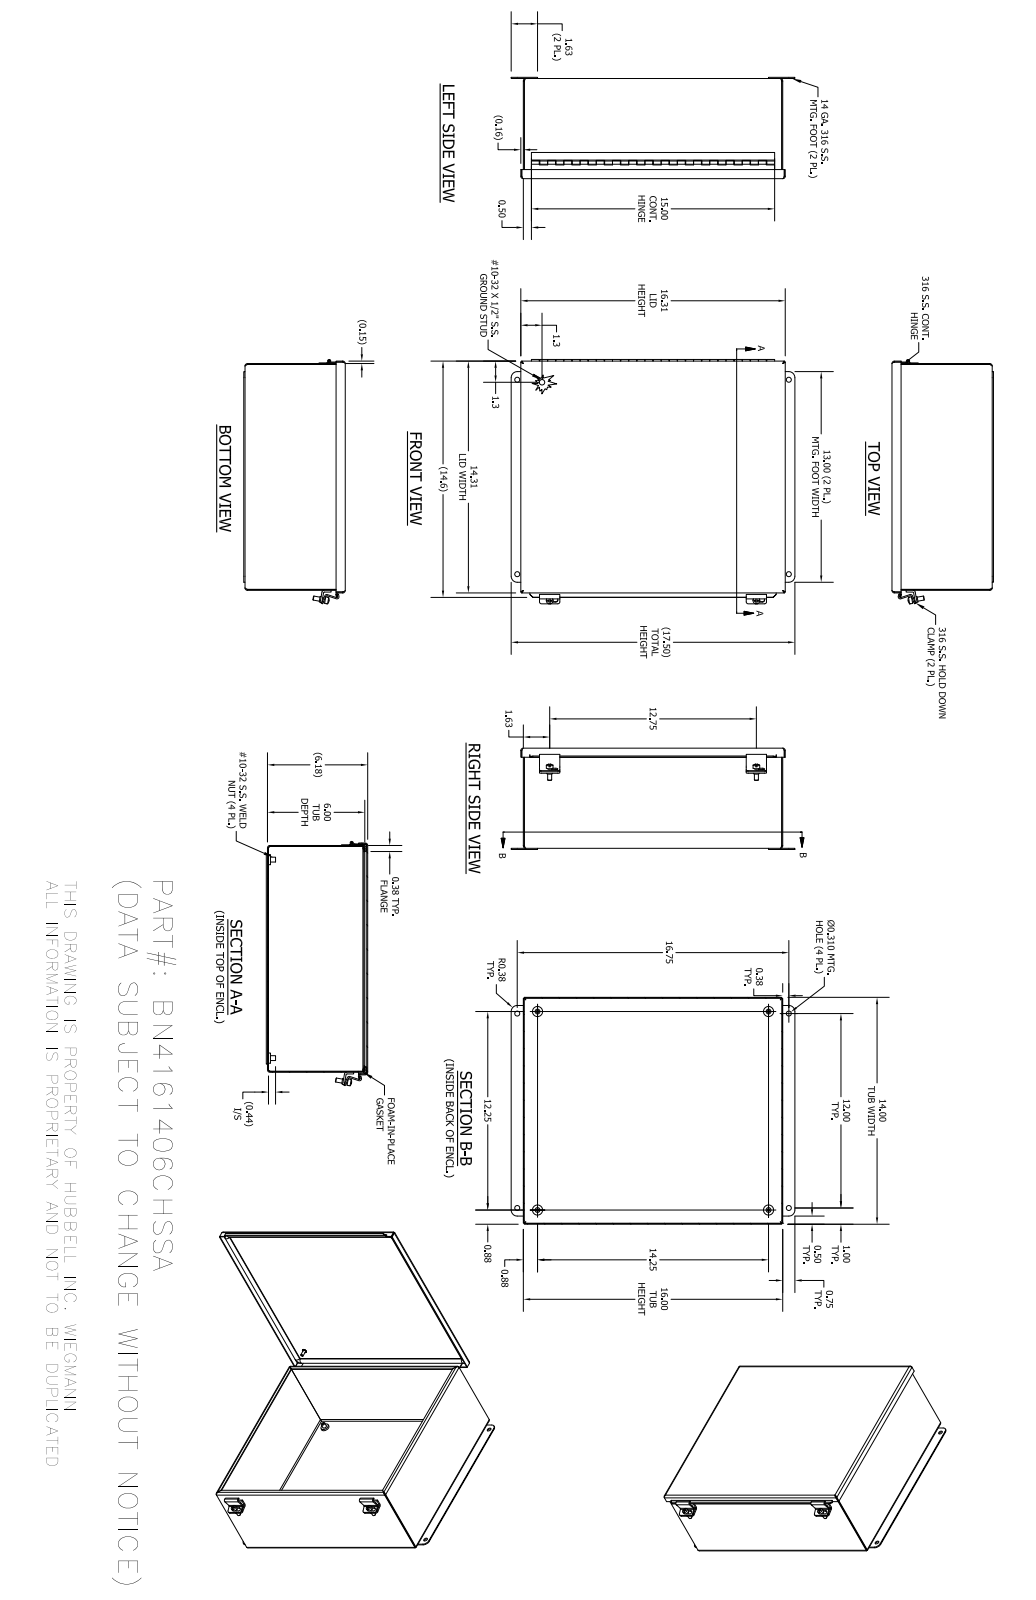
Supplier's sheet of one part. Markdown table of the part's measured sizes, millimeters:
| quantity | value |
| --- | --- |
| part name | B_161406_SSABKP; 32886LH; 32886P; 32886TH (+8 more) |
| STEP written by | Autodesk Inventor 2016 (AUTOMOTIVE_DESIGN) |
| units | millimeters |
| bodies | 19 solids, 508 faces (280 planar, 161 cylindrical, 67 other) |
| overall size | 444.5 × 383.18 × 158.91 |
| volume | 993 799 mm³ |
| surface area | 1 263 000 mm² |
| round holes (diameter × count) | 2.79 × 4, 3.96 × 4, 7.87 × 4, 4.98 × 2, 2.96 × 1 |
| round bosses / shafts (diameter × count) | 15.88 × 4, 7.62 × 4, 10.4 × 2, 8.74 × 2, 6.35 × 2, 8.56 × 1, 5.08 × 1, 4.83 × 1 |
| partial cylindrical surfaces (radius × count) | 2.38 × 13, 3.88 × 13, 1.68 × 8, 3.17 × 8, 3.38 × 4, 5.78 × 4, 9.53 × 4, 1.6 × 3 |
| main face-to-face distances | 1.5, 155.51, 157.01, 154.01, 354.1, 404.9, 355.6, 352.6, 406.4, 403.4 |
| hole center spacings | 309.61, 31.91, 304.8, 323.85, 393.71, 499.85, 19.05, 311.16 |
